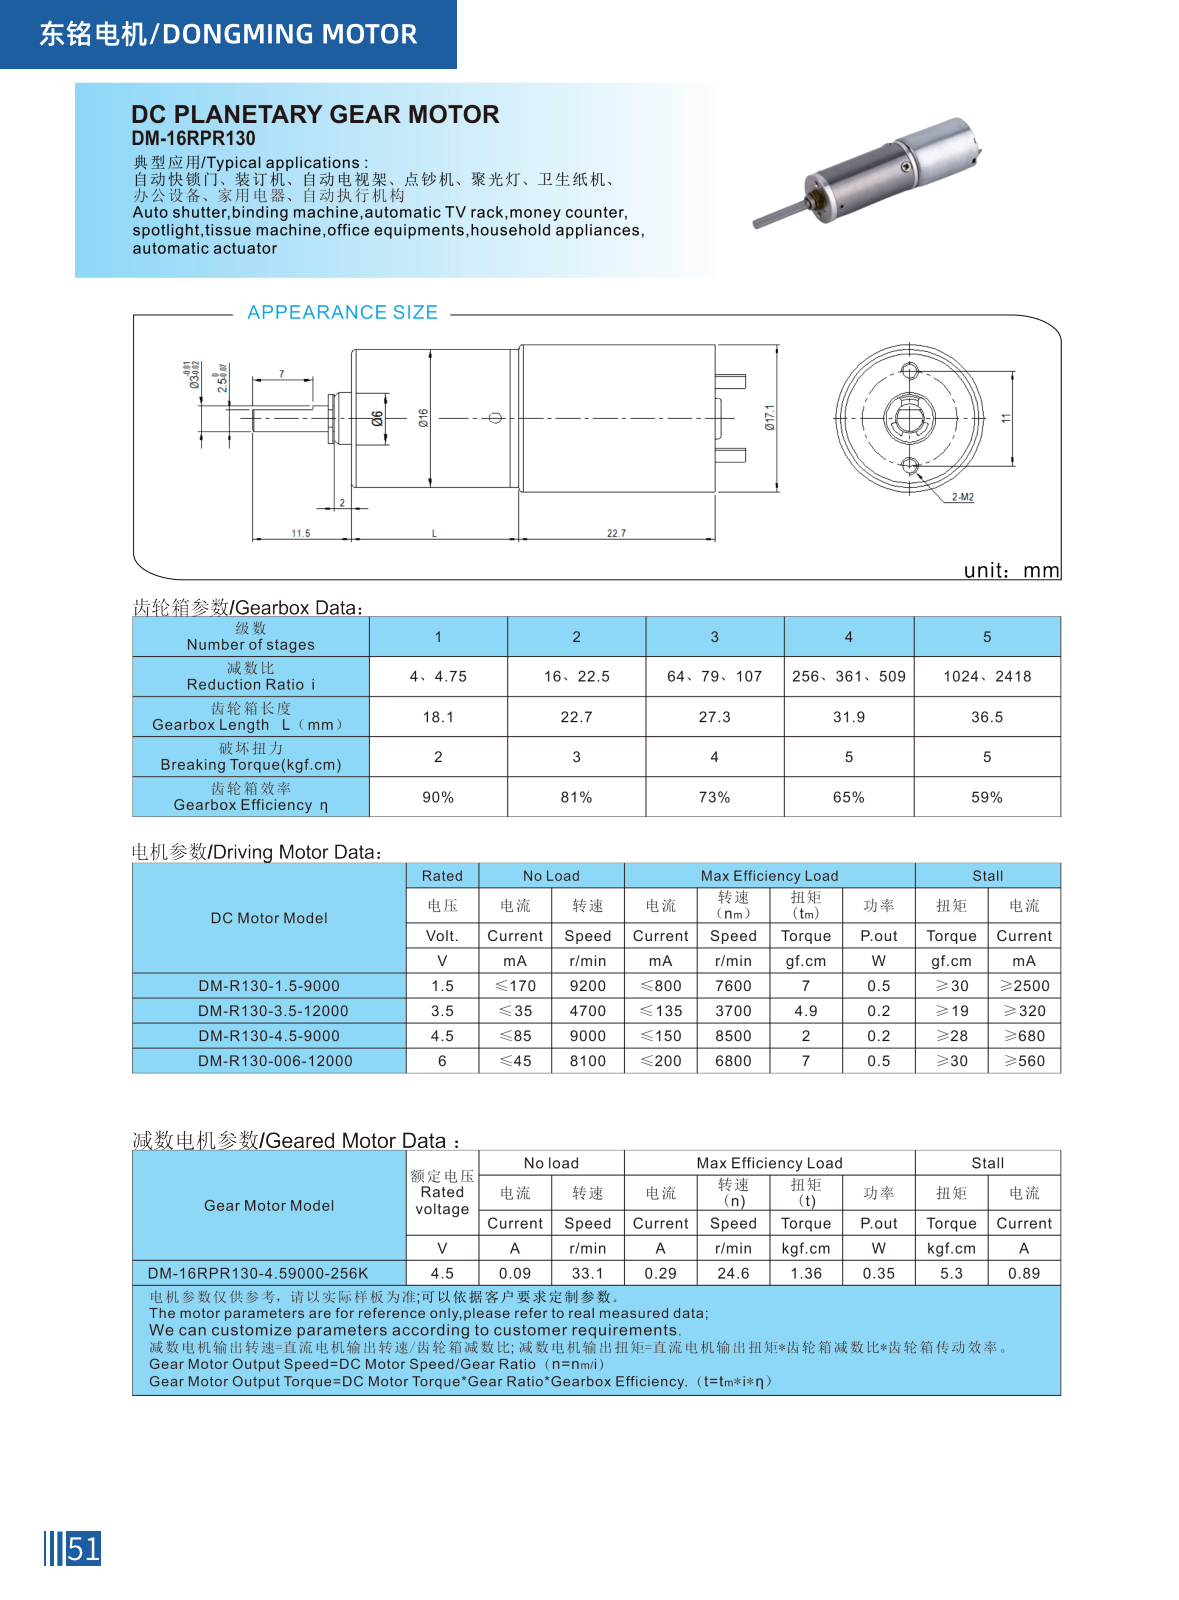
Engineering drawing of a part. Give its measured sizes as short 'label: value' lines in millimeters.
name: PRT0024; PRT0025; ASM0009_ASM_ASM; PRT0026 (+8 more)
written by: PRO/ENGINEER BY PARAMETRIC TECHNOLOGY CORPORATION, 2010280 (CONFIG_CONTROL_DESIGN)
unit: mm
bodies: 19 solids, 1207 faces (449 planar, 473 cylindrical, 285 other)
size: 69 × 17.1 × 17.1
volume: 8 929 mm³; area: 8 528 mm²
holes: 4× ⌀1.5, 4× ⌀1.6, 4× ⌀2, 3× ⌀0.9, 2× ⌀1.25, 1× ⌀2.5, 1× ⌀3, 1× ⌀3.5, 1× ⌀4.75, 1× ⌀14.5
bosses: 3× ⌀2, 2× ⌀3.5, 2× ⌀2.9, 2× ⌀1.6, 2× ⌀1.1, 1× ⌀17.1, 1× ⌀16, 1× ⌀12.8
rounds: 96× R0.1, 30× R0.11, 4× R0.3, 4× R1, 4× R1.05, 2× R0.36, 2× R0.4, 2× R1.25
face distances: 5.5, 26.4, 22.8, 23.6, 31.9, 54.7, 2.5, 49.2, 5.8, 2.8
hole spacings: 4.05, 5.01, 5.5, 9.71, 10.01, 11, 24.8
